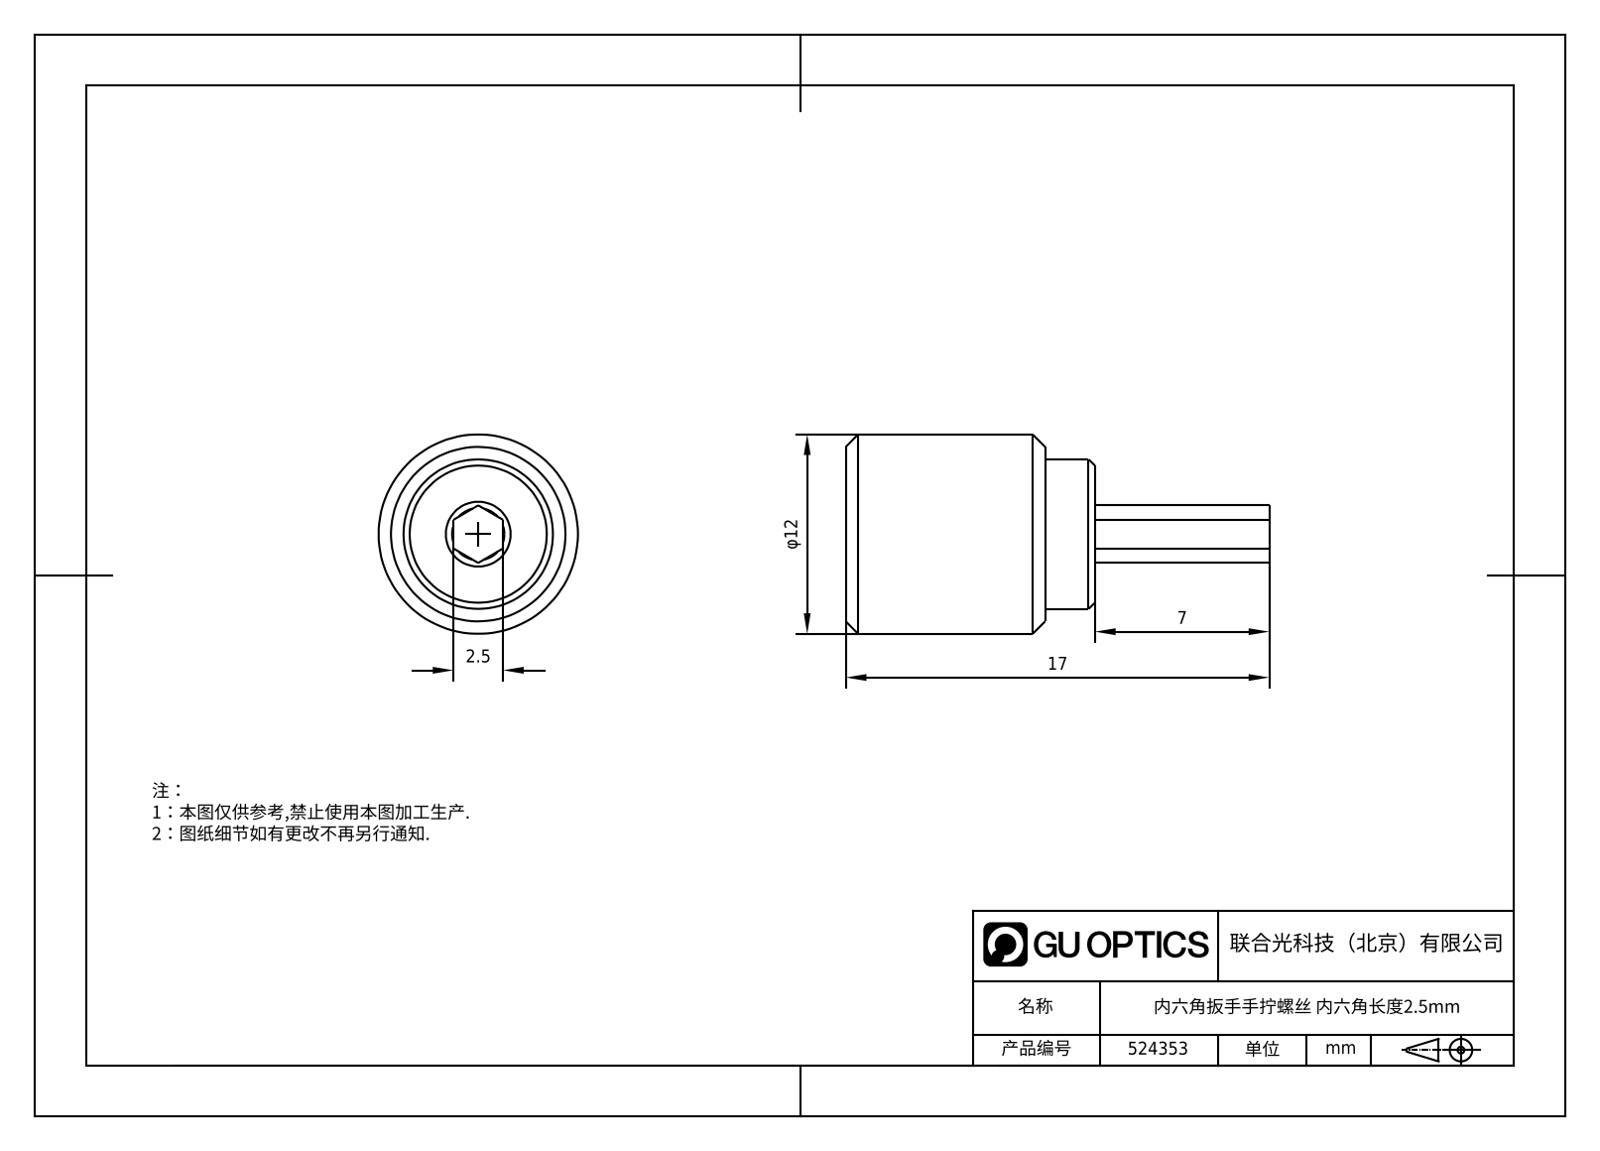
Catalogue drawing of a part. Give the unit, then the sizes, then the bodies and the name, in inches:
Units: inches
Overall size (bounding box): 0.669 × 0.472 × 0.472
Round holes (diameter × count): ⌀0.106 ×1
Round bosses / shafts (diameter × count): ⌀0.472 ×1, ⌀0.394 ×1
Main face-to-face distances: 0.394, 0.098, 0.079, 0.315, 0.236, 0.157, 0.669, 0.433, 0.354, 0.276
Volume: 0.066 in³ · Surface area: 1.09 in²
Bodies: 2 solids, 26 faces (12 planar, 6 cylindrical, 8 other)
Part name (STEP PRODUCT): 直杆式六角扳手_1.8.4.4.2
STEP written by: SolidWorks 2021 (CONFIG_CONTROL_DESIGN)
